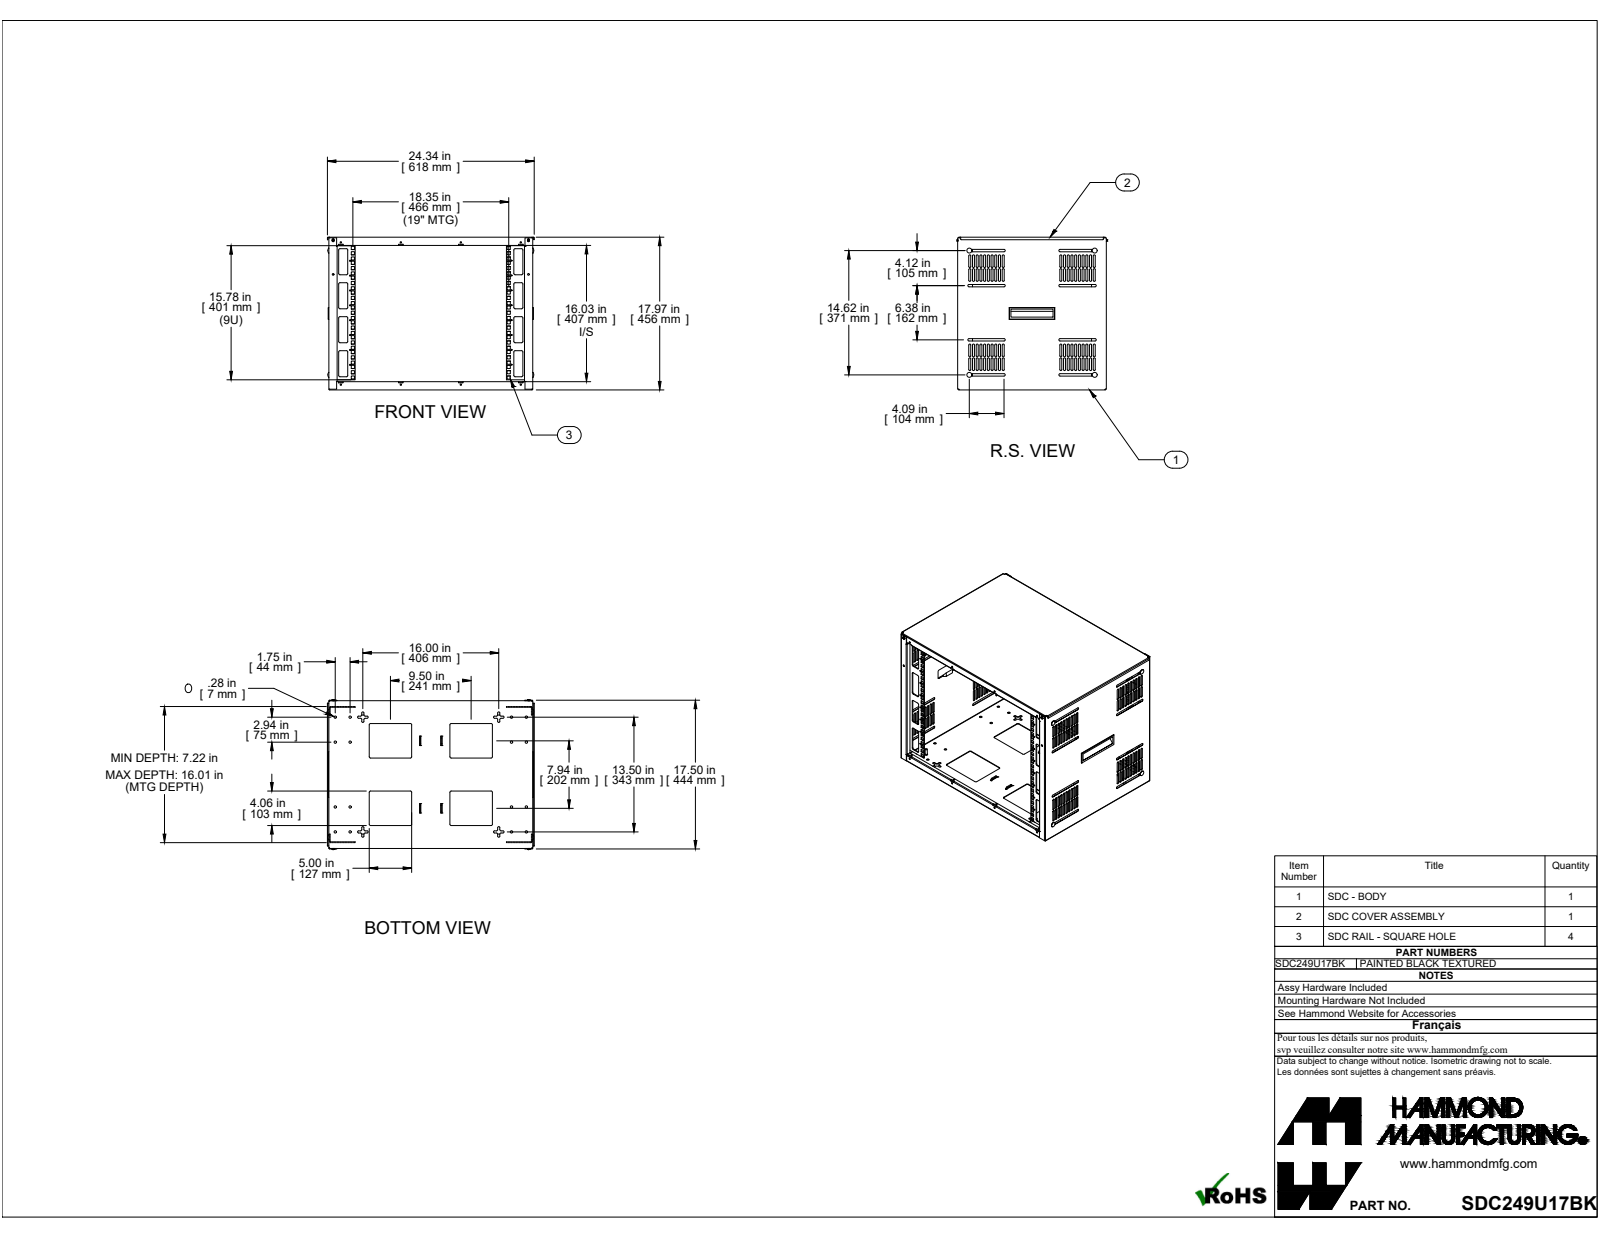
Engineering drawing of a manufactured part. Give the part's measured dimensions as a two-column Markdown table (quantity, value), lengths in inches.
| quantity | value |
| --- | --- |
| part name | SDC249U17BK |
| STEP written by | SolidWorks 2019 (CONFIG_CONTROL_DESIGN) |
| units | inches |
| bodies | 36 solids, 2490 faces (1630 planar, 808 cylindrical, 52 other) |
| overall size | 24.344 × 17.972 × 17.67 |
| volume | 111.8 in³ |
| surface area | 3 715 in² |
| round holes (diameter × count) | 0.125 × 32, 0.17 × 16, 0.281 × 16, 0.196 × 4, 0.159 × 2, 0.187 × 2, 0.213 × 2 |
| round bosses / shafts (diameter × count) | 0.25 × 8, 0.58 × 4, 0.313 × 2, 0.28 × 2, 0.187 × 2, 0.138 × 2 |
| partial cylindrical surfaces (radius × count) | 0.118 × 160, 0.157 × 68, 0.029 × 22, 0.086 × 22, 0.025 × 16, 0.125 × 16, 0.141 × 16, 0.117 × 12 |
| main face-to-face distances | 0.057, 17.915, 23.943, 17.858, 17.972, 23.886, 24, 0.912, 0.095, 15.919 |
| hole center spacings | 1.75, 19.085, 3.5, 5.25, 19.005, 2.937, 3.419, 7 |
